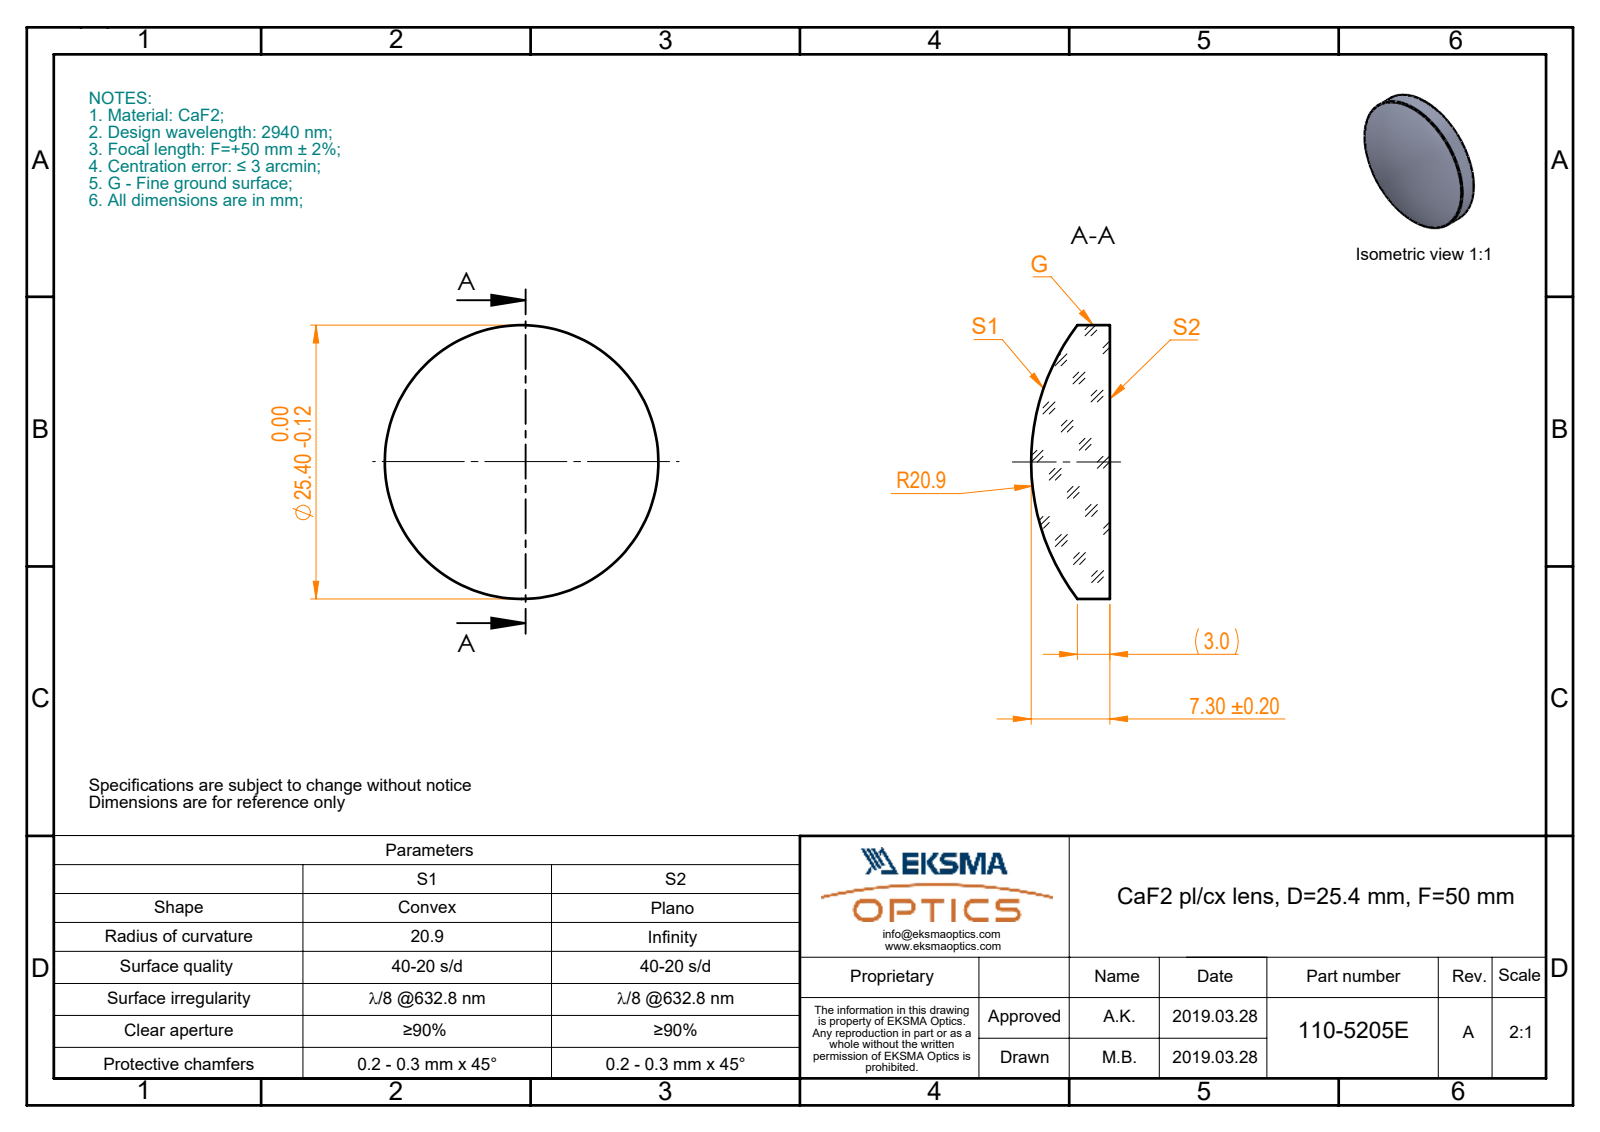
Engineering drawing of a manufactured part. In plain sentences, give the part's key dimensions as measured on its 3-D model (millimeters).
The part is named "110-5205E CaF2 pl-cx 25.4 F50". Its 3-D file was written by "SolidWorks 2017 (CONFIG_CONTROL_DESIGN)". It is 1 solid with 5 faces: 1 planar, 2 cylindrical and 2 other. Overall it measures 25.4 by 25.4 by 5.7 millimeters. Its volume is 2 218 cubic millimeters and its surface area 1 277 square millimeters. Round bosses or shafts: 1 of diameter 25.4.
